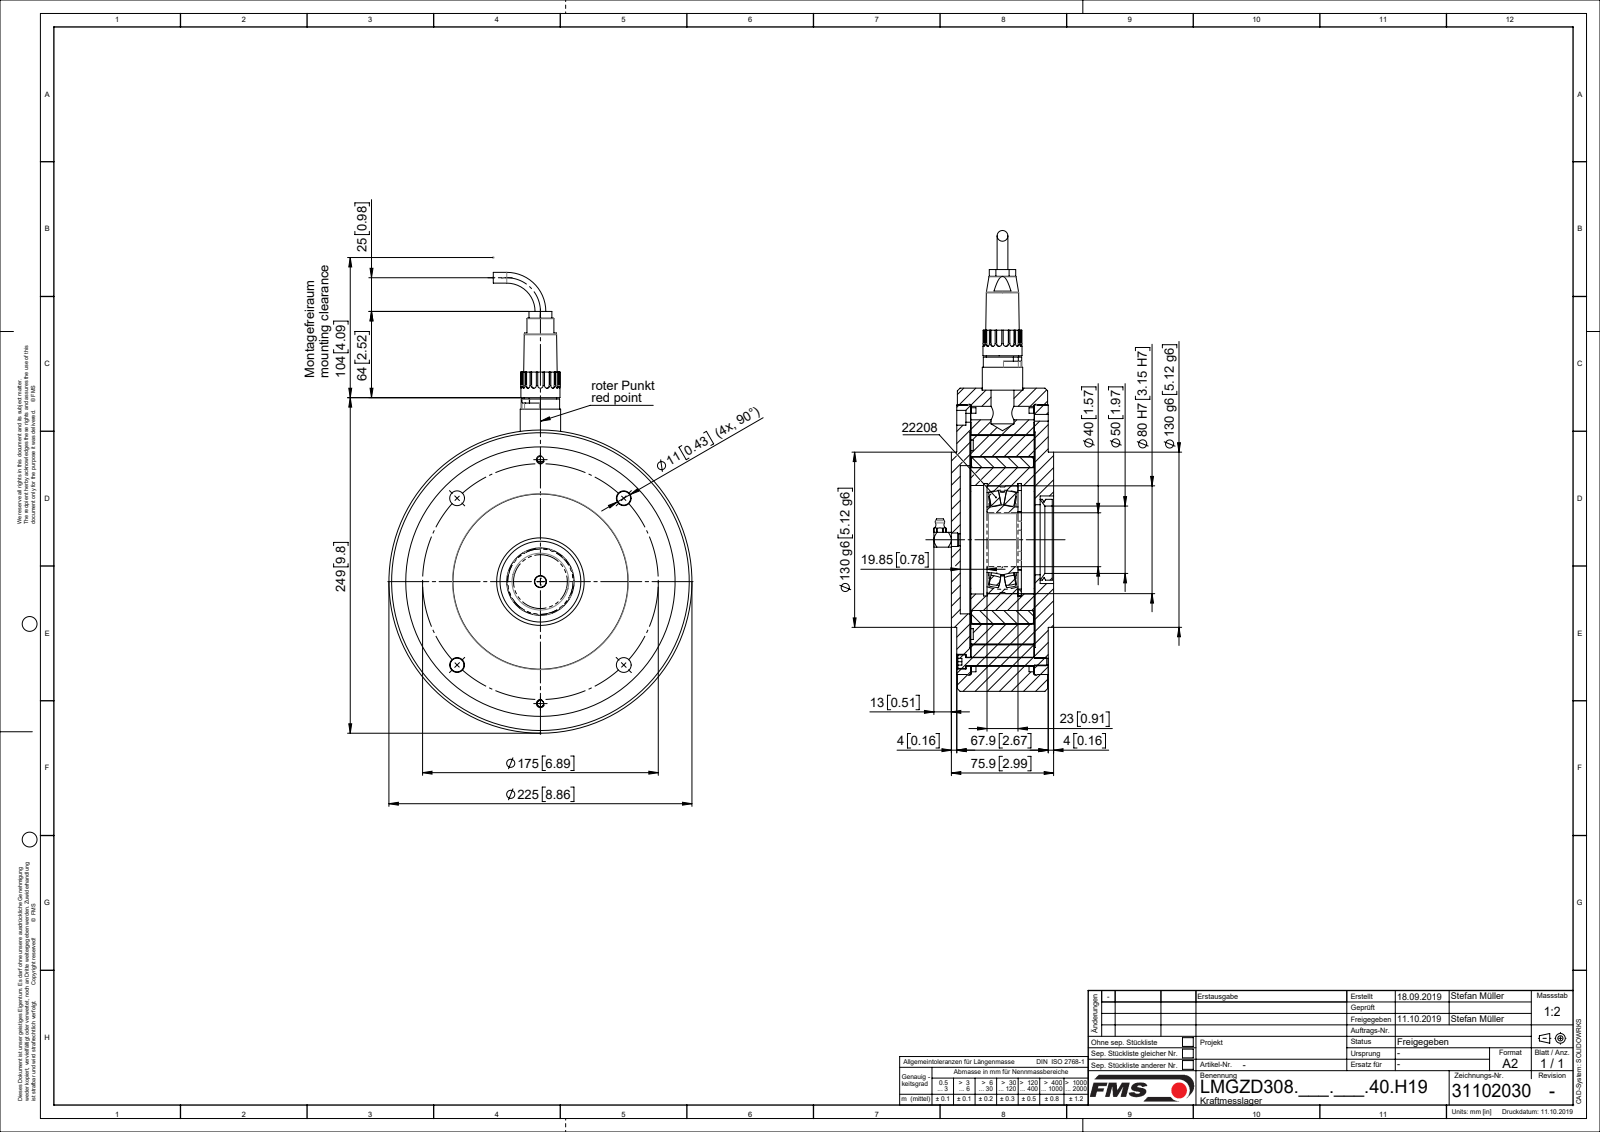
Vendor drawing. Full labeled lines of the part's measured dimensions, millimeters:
Part name (STEP PRODUCT): Kabeldose_Kunstst_7pol_01; 31102030_stp; Zyl-Schr DIN912_M6x60; 31102024_01 (+8 more)
STEP written by: SolidWorks 2018 (CONFIG_CONTROL_DESIGN)
Units: millimetres
Bodies: 51 solids, 882 faces (241 planar, 352 cylindrical, 289 other)
Overall size (bounding box): 342 × 225 × 88.9
Volume: 2 419 000 mm³ · Surface area: 455 170 mm²
Round holes (diameter × count): ⌀11 ×6, ⌀2.5 ×4, ⌀3.2 ×3, ⌀3 ×2, ⌀3.4 ×2, ⌀3.6 ×2, ⌀5 ×2, ⌀6.6 ×2, ⌀10 ×2, ⌀10.2 ×2, ⌀8 ×1, ⌀9 ×1
Round bosses / shafts (diameter × count): ⌀2.15 ×7, ⌀10 ×2, ⌀5.5 ×2, ⌀3 ×2, ⌀225 ×1, ⌀199 ×1, ⌀188 ×1, ⌀132 ×1
Partial cylindrical surfaces — rounded edges, fillets, slot ends (radius × count): R2 ×17, R0.1 ×4, R11 ×4, R3 ×2, R4.91 ×2, R4.5 ×1, R33.25 ×1, R79 ×1
Main face-to-face distances: 47.25, 10.2, 10.45, 57.45, 57.7, 48, 0.75, 0.5, 47.75, 9.7
Hole centre spacings: 16.26, 22.47, 23, 62.02, 68.17, 87.5, 123.74, 134.45
